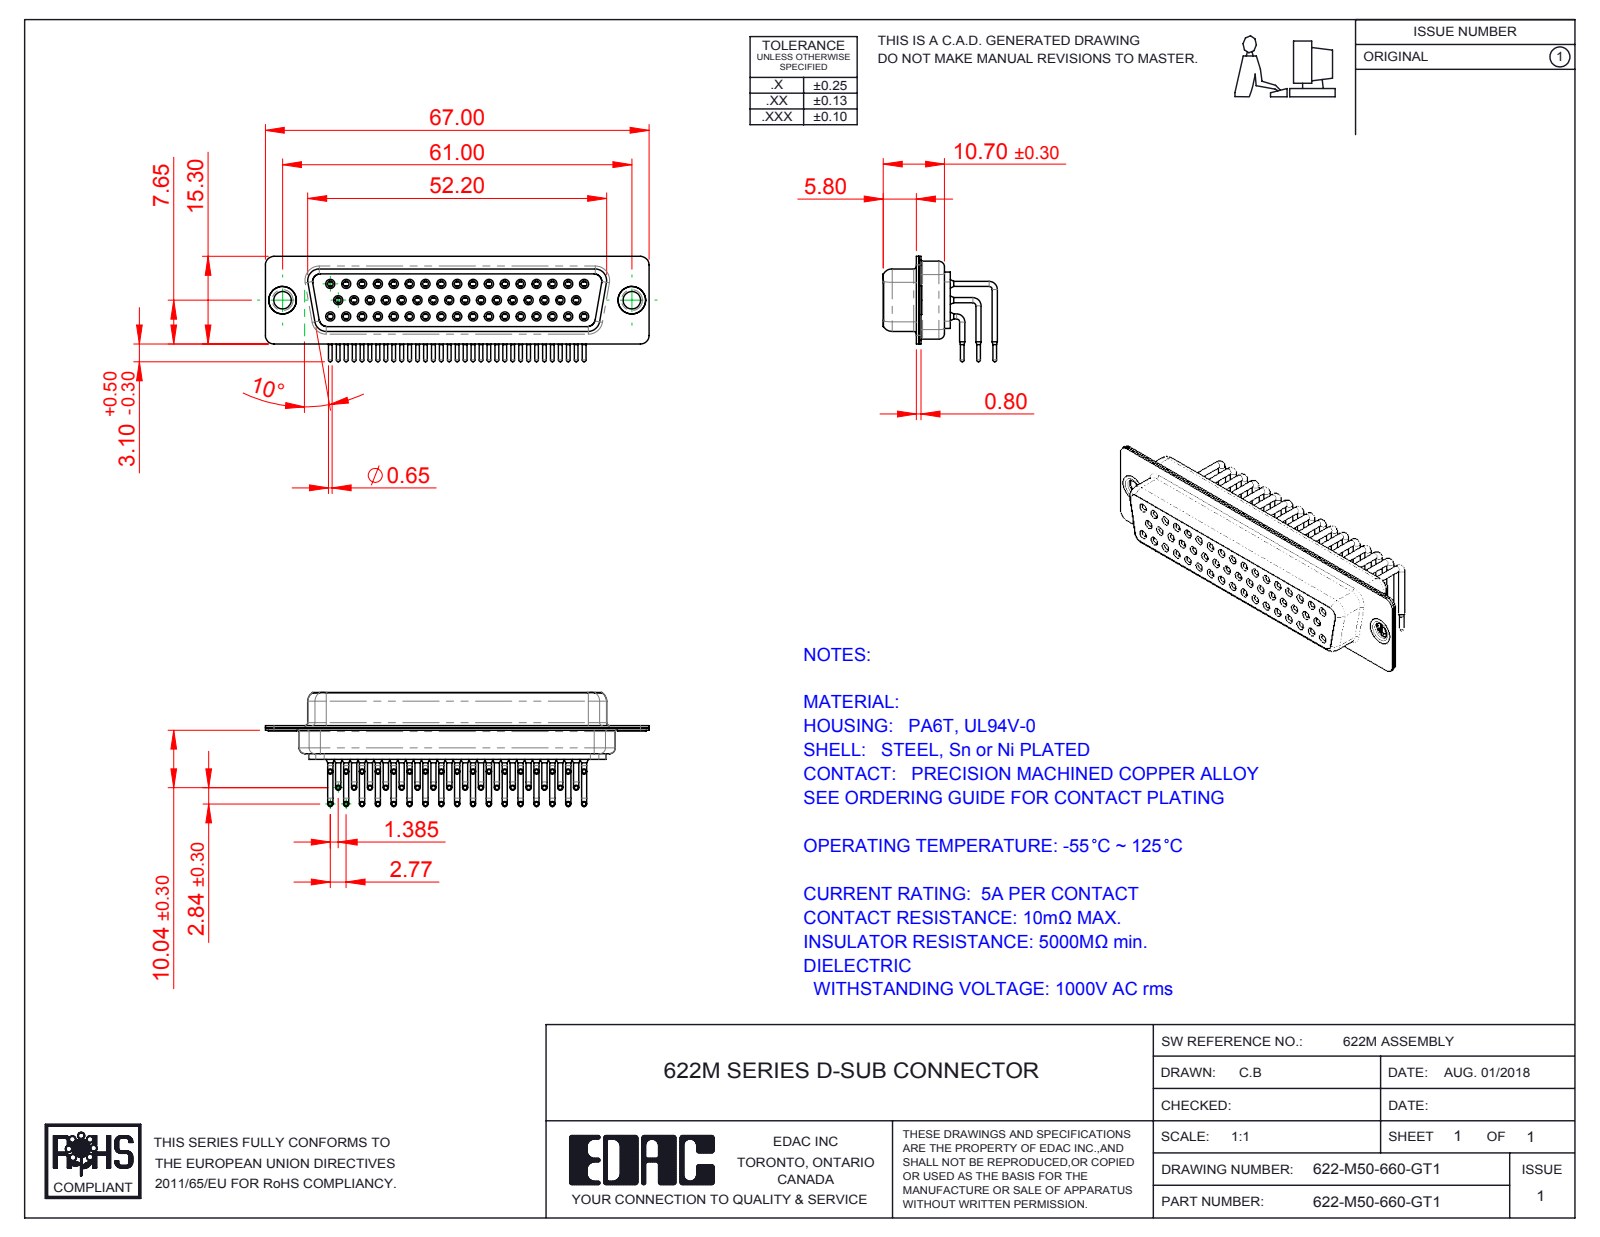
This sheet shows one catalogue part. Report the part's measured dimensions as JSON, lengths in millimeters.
{"part_name": "622M Thru Hole Rivet; 622M Contact Row 3; 622M Contact Row 2_50 Contacts; 622M Contact Row 1_50 Contacts (+4 more)", "step_written_by": "SolidWorks 2016 (CONFIG_CONTROL_DESIGN)", "units": "millimeters", "bodies": {"solids": 55, "faces": 2903, "planar": 817, "cylindrical": 1271, "other": 815}, "overall_size": [67, 19.93, 18.4], "volume_mm3": 6854, "surface_area_mm2": 15982, "round_holes": [[1, 50], [1.1, 50], [1.7, 50], [1.8, 50], [2, 50], [3.05, 2], [4, 2], [4.8, 2]], "round_bosses_or_shafts": [[0.9, 100], [1.6, 50], [1.5, 50], [0.65, 50], [5, 2], [4.9, 2], [3.55, 2]], "partial_cylinders_radius": [[1.5, 16], [2, 12], [1.35, 8], [1.6, 8], [0.25, 4], [0.5, 4], [0.6, 4], [0.65, 4]], "face_to_face_distances": [0.4, 1.35, 11.85, 0.85, 2.2, 5.5, 12.25, 5.9, 10.5, 10.05], "hole_center_spacings": [2.77, 3.16, 5.54, 8.31, 11.08, 13.85, 16.62, 19.39]}
